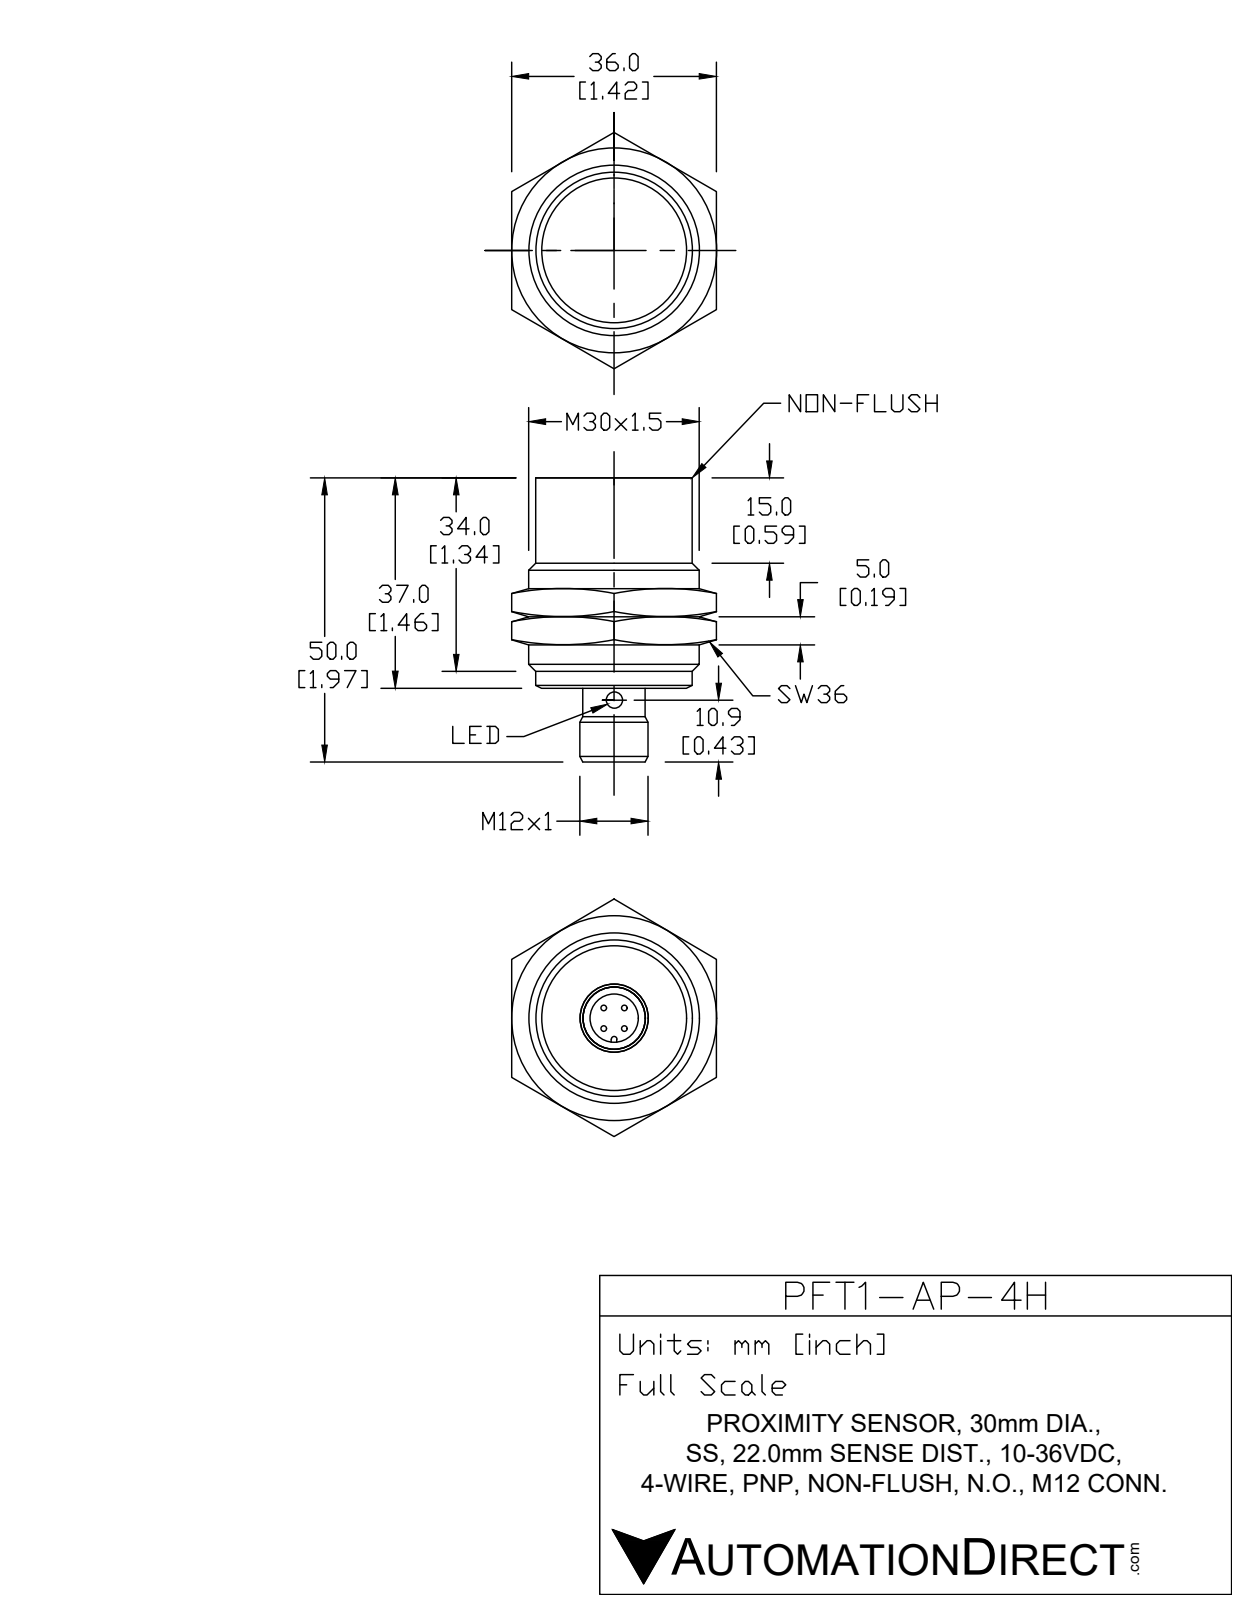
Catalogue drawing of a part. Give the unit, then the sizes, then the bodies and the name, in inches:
Units: inches
Overall size (bounding box): 1.969 × 1.637 × 1.417
Round holes (diameter × count): ⌀0.098 ×2, ⌀0.331 ×1, ⌀1.117 ×1
Round bosses / shafts (diameter × count): ⌀1.181 ×1, ⌀1.083 ×1, ⌀0.472 ×1, ⌀0.433 ×1
Partial cylindrical surfaces — rounded edges, fillets, slot ends (radius × count): R0.024 ×1, R0.189 ×1
Main face-to-face distances: 0.197, 0.984, 1.417, 0.472, 1.457, 1.181, 0.787, 0.669, 0.394, 0.276
Volume: 1.798 in³ · Surface area: 14.31 in²
Bodies: 3 solids, 99 faces (27 planar, 32 cylindrical, 40 other)
Part name (STEP PRODUCT): PFT1-AP-4H
STEP written by: SolidWorks 2017 (AUTOMOTIVE_DESIGN)
